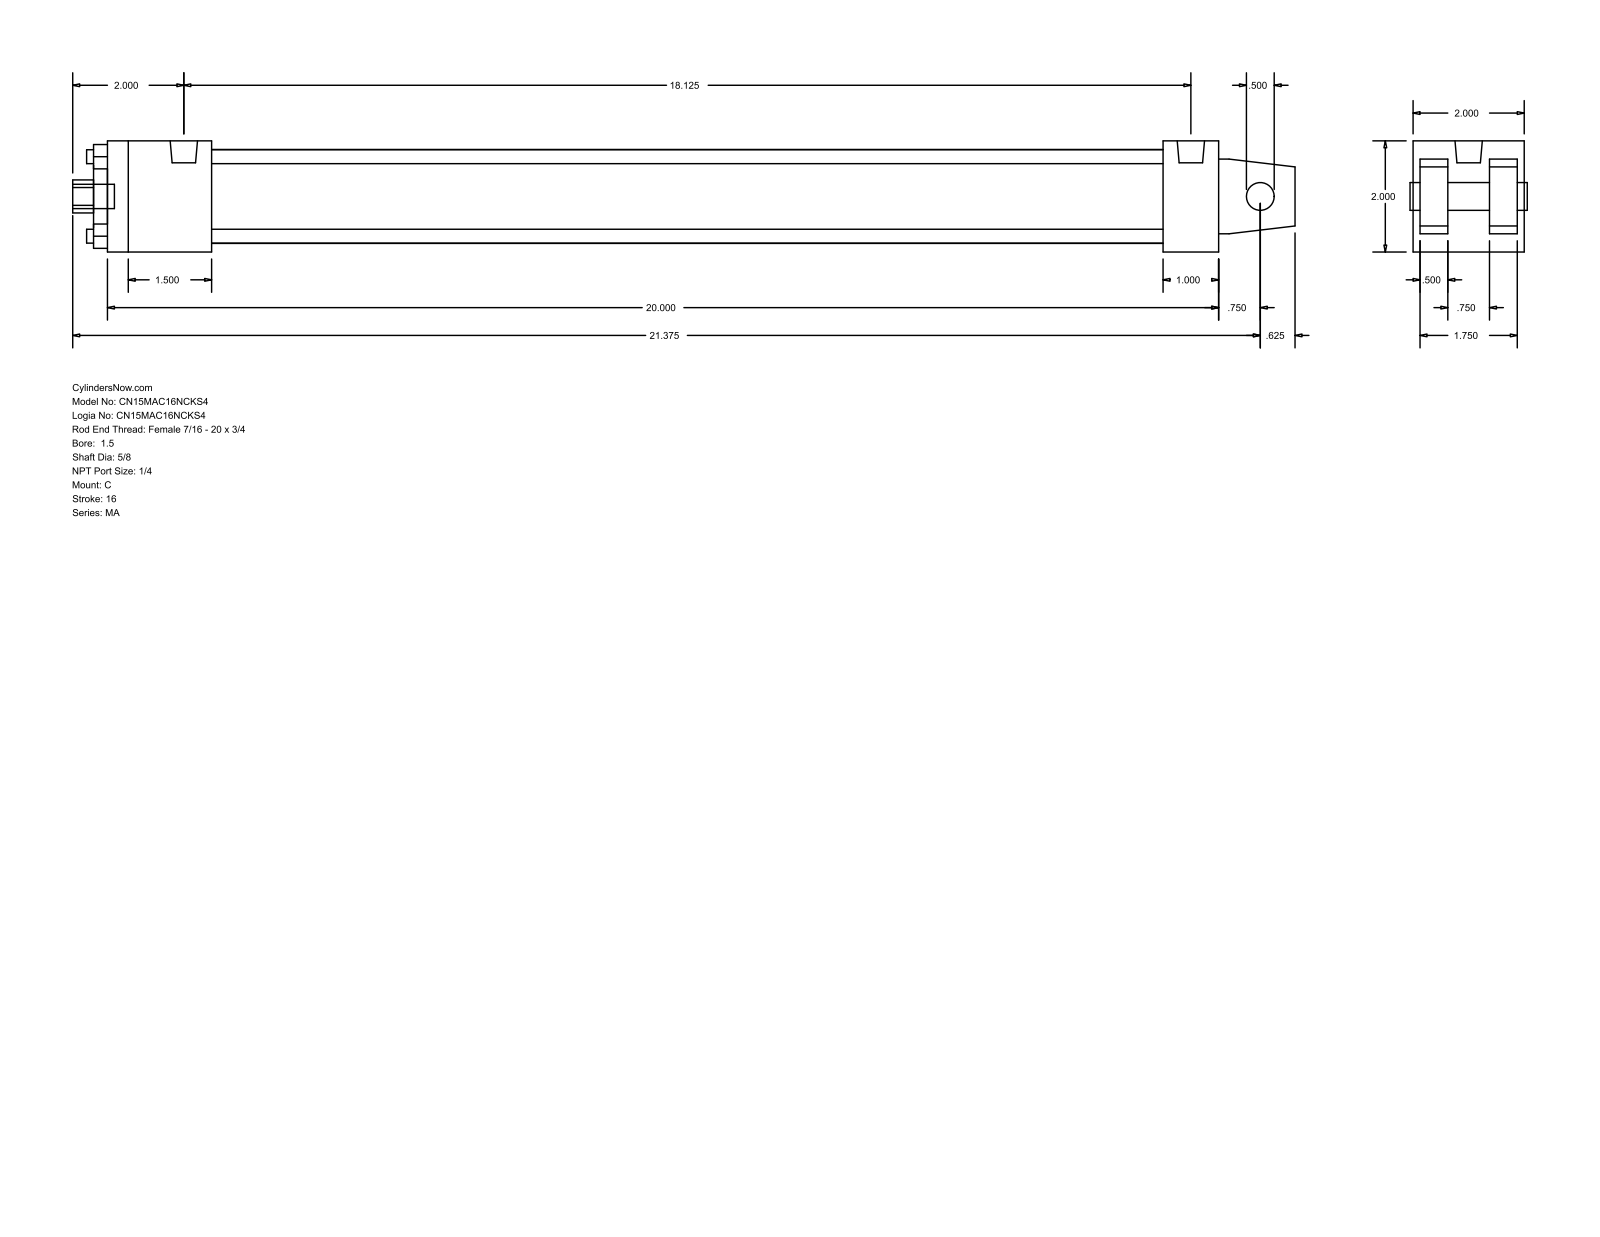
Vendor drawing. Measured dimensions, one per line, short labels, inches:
name: MA_C__0150_0.625
written by: GSSL Pune (CONFIG_CONTROL_DESIGN)
unit: in
bodies: 0 solids, 103 faces (76 planar, 27 cylindrical, 0 other)
size: 22 × 2 × 2
holes: 4× ⌀0.25, 1× ⌀0.5, 1× ⌀0.625, 1× ⌀1.125, 1× ⌀1.69
bosses: 4× ⌀0.313, 2× ⌀0.492, 1× ⌀0.437
rounds: 1× R0.297
face distances: 2, 0.5, 0.125, 0.625, 1.375, 1.875, 1.25, 20, 19, 1
hole spacings: 1.011, 1.43, 2.022
